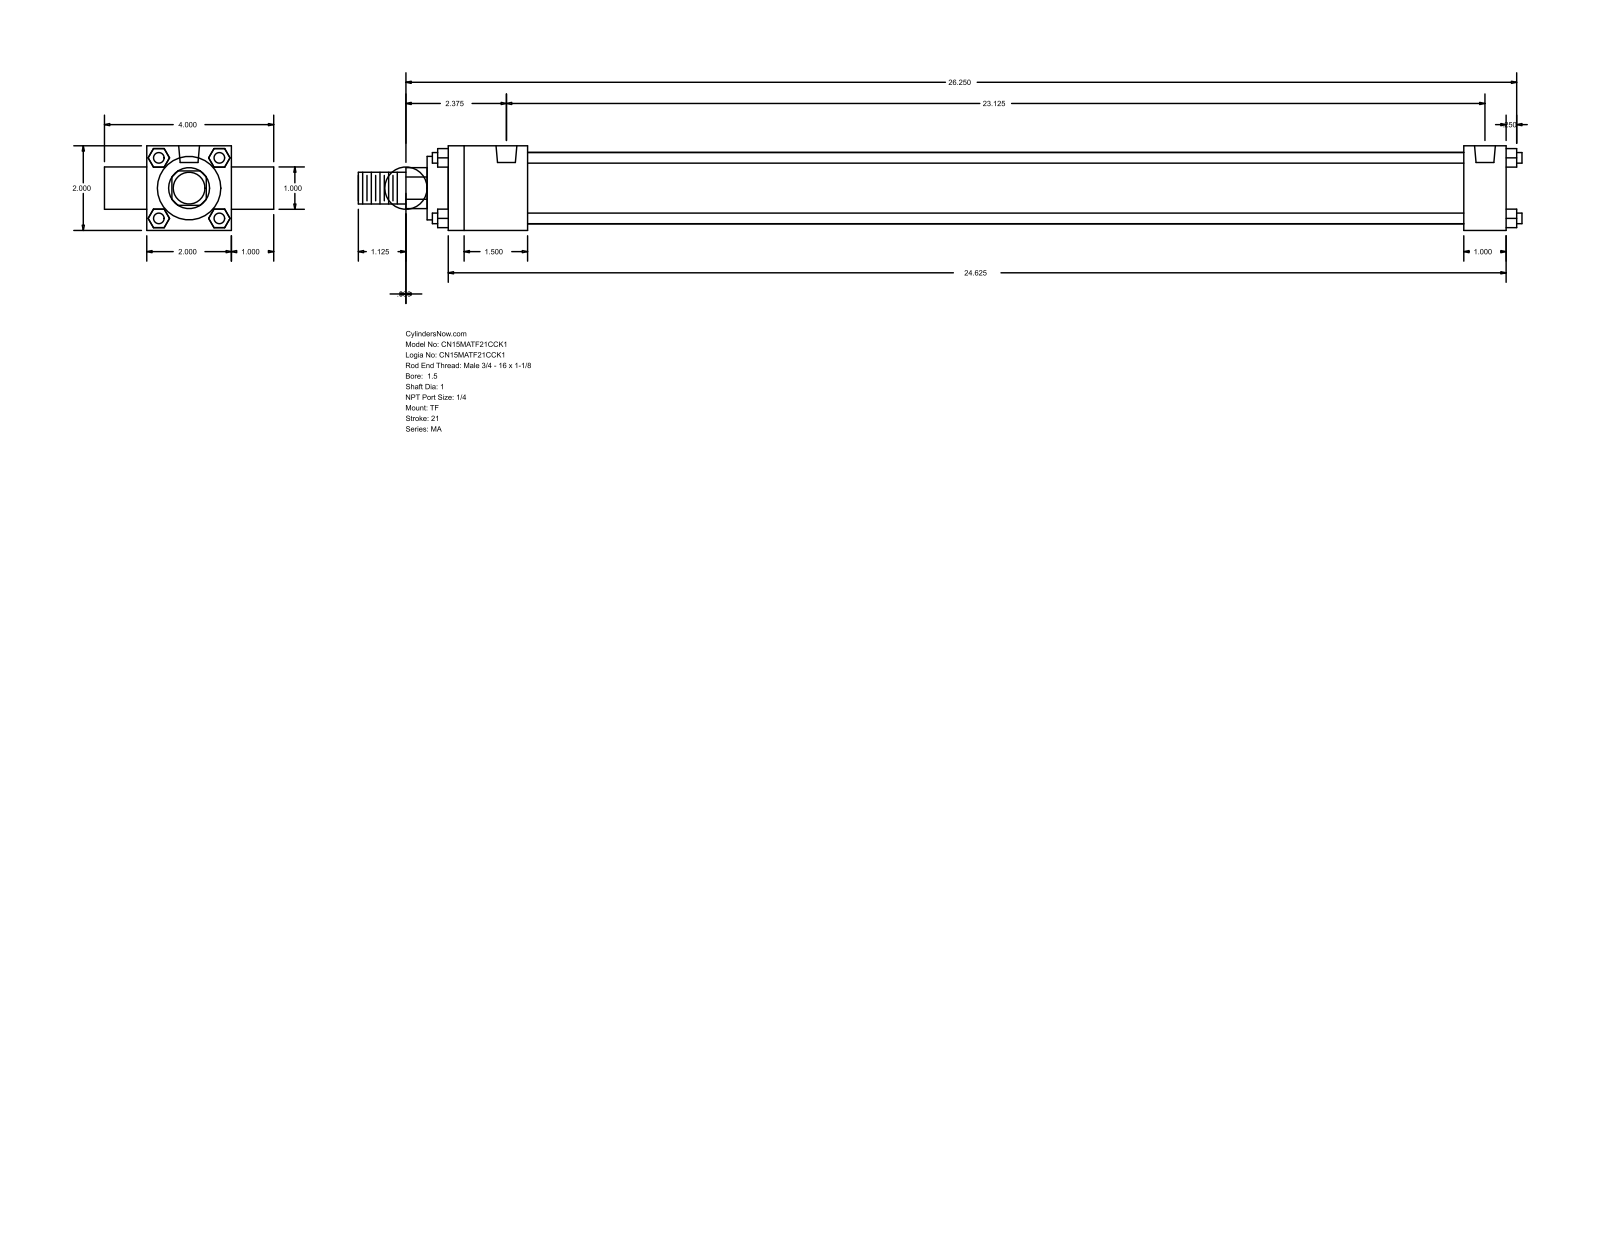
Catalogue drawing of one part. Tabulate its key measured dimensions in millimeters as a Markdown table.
| quantity | value |
| --- | --- |
| part name | MA_TF__0150_1 |
| STEP written by | GSSL Pune (CONFIG_CONTROL_DESIGN) |
| units | millimeters |
| bodies | 0 solids, 120 faces (92 planar, 28 cylindrical, 0 other) |
| overall size | 698.5 × 101.6 × 50.8 |
| round holes (diameter × count) | 7.94 × 3, 12.49 × 2 |
| round bosses / shafts (diameter × count) | 6.35 × 4, 25.4 × 2, 42.93 × 1, 38.1 × 1, 19.05 × 1 |
| partial cylindrical surfaces (radius × count) | 12.29 × 1 |
| main face-to-face distances | 50.8, 25.4, 635, 76.2, 6.35, 47.63, 609.6, 561.97, 587.37, 647.7 |
| hole center spacings | 587.37 |
